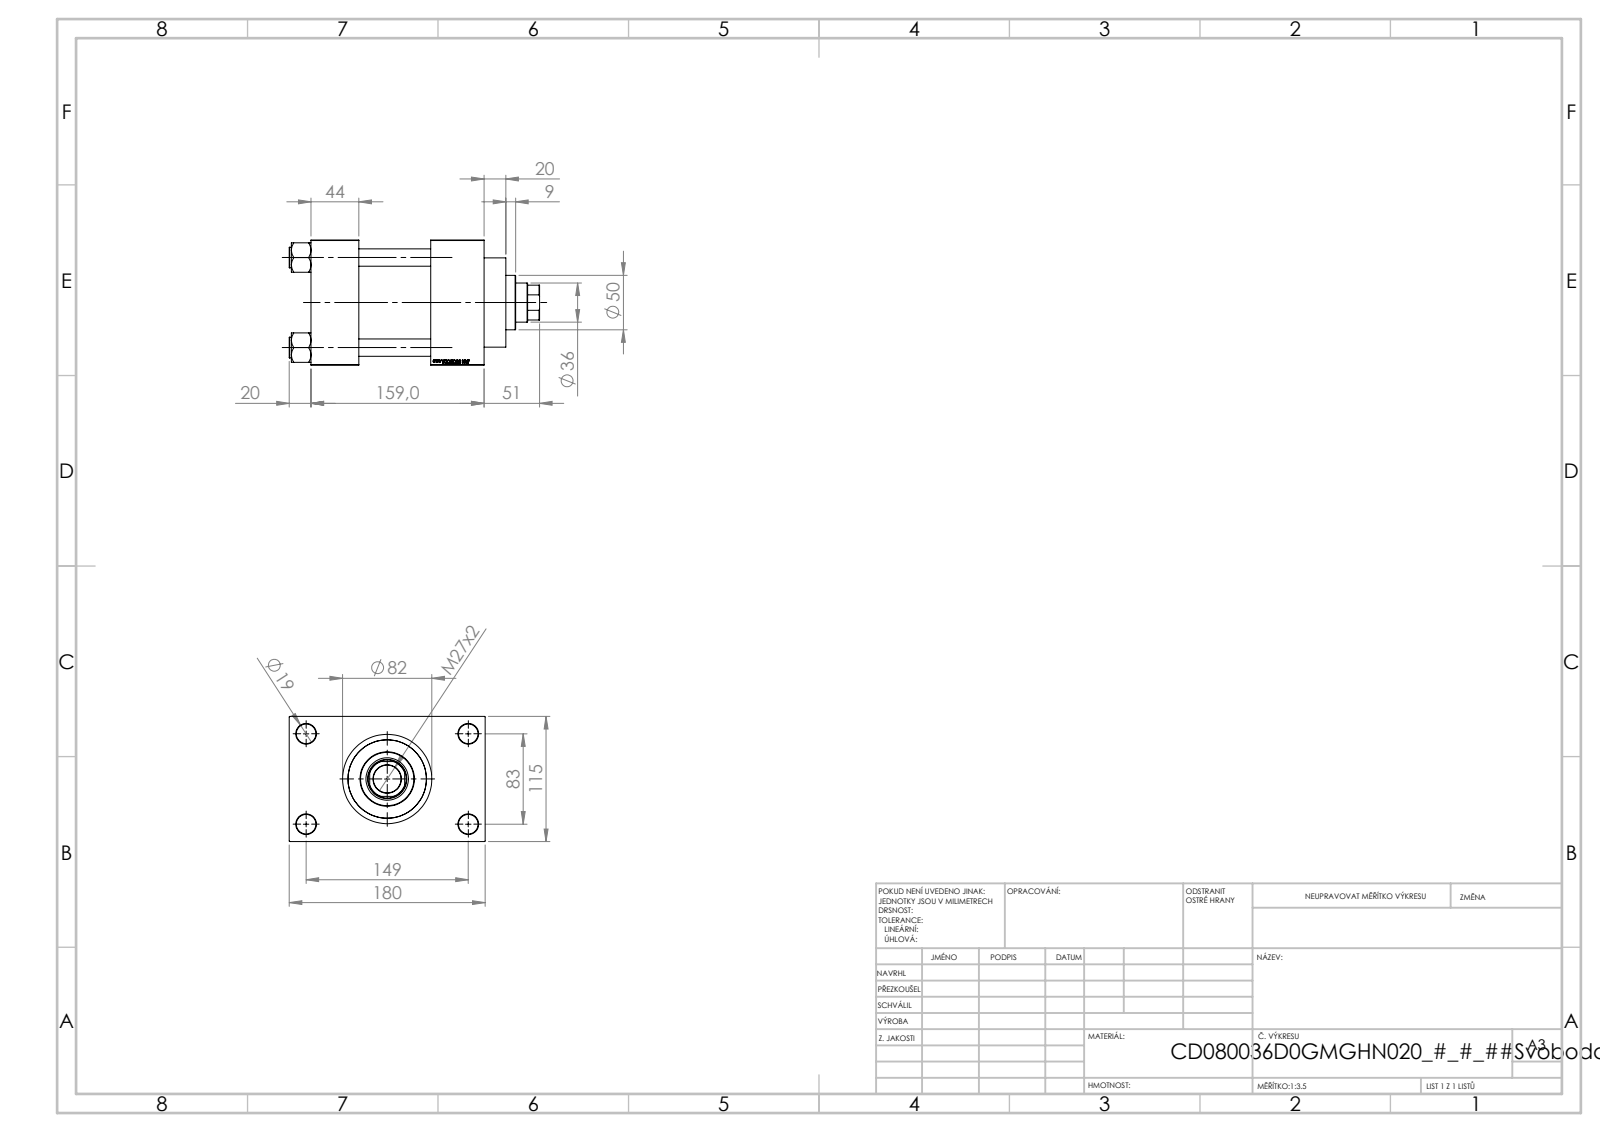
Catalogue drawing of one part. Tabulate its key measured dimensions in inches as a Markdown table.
| quantity | value |
| --- | --- |
| part name | V215CD_NUT_M5_D; V215CD_VC_A; V215CD_D_TYCINKA; V215CD_VCP_D (+1 more) |
| STEP written by | SolidWorks 2019 (CONFIG_CONTROL_DESIGN) |
| units | inches |
| bodies | 11 solids, 1151 faces (545 planar, 88 cylindrical, 518 other) |
| overall size | 9.055 × 7.087 × 4.528 |
| volume | 120.8 in³ |
| surface area | 459.5 in² |
| round holes (diameter × count) | 0.63 × 4, 0.709 × 4, 0.276 × 2, 1.041 × 2, 1.378 × 2, 1.004 × 1, 1.417 × 1, 1.535 × 1, 2.402 × 1, 2.835 × 1, 3.15 × 1 |
| round bosses / shafts (diameter × count) | 0.748 × 4, 3.386 × 1, 3.228 × 1, 1.969 × 1 |
| partial cylindrical surfaces (radius × count) | 0.689 × 1 |
| main face-to-face distances | 4.528, 2.598, 4.331, 1.929, 1.732, 6.26, 1.28, 5.807, 0.787, 2.717 |
| hole center spacings | 1.305, 2.302, 3.256, 3.357, 3.513, 4.561, 5.607, 3.268 |
